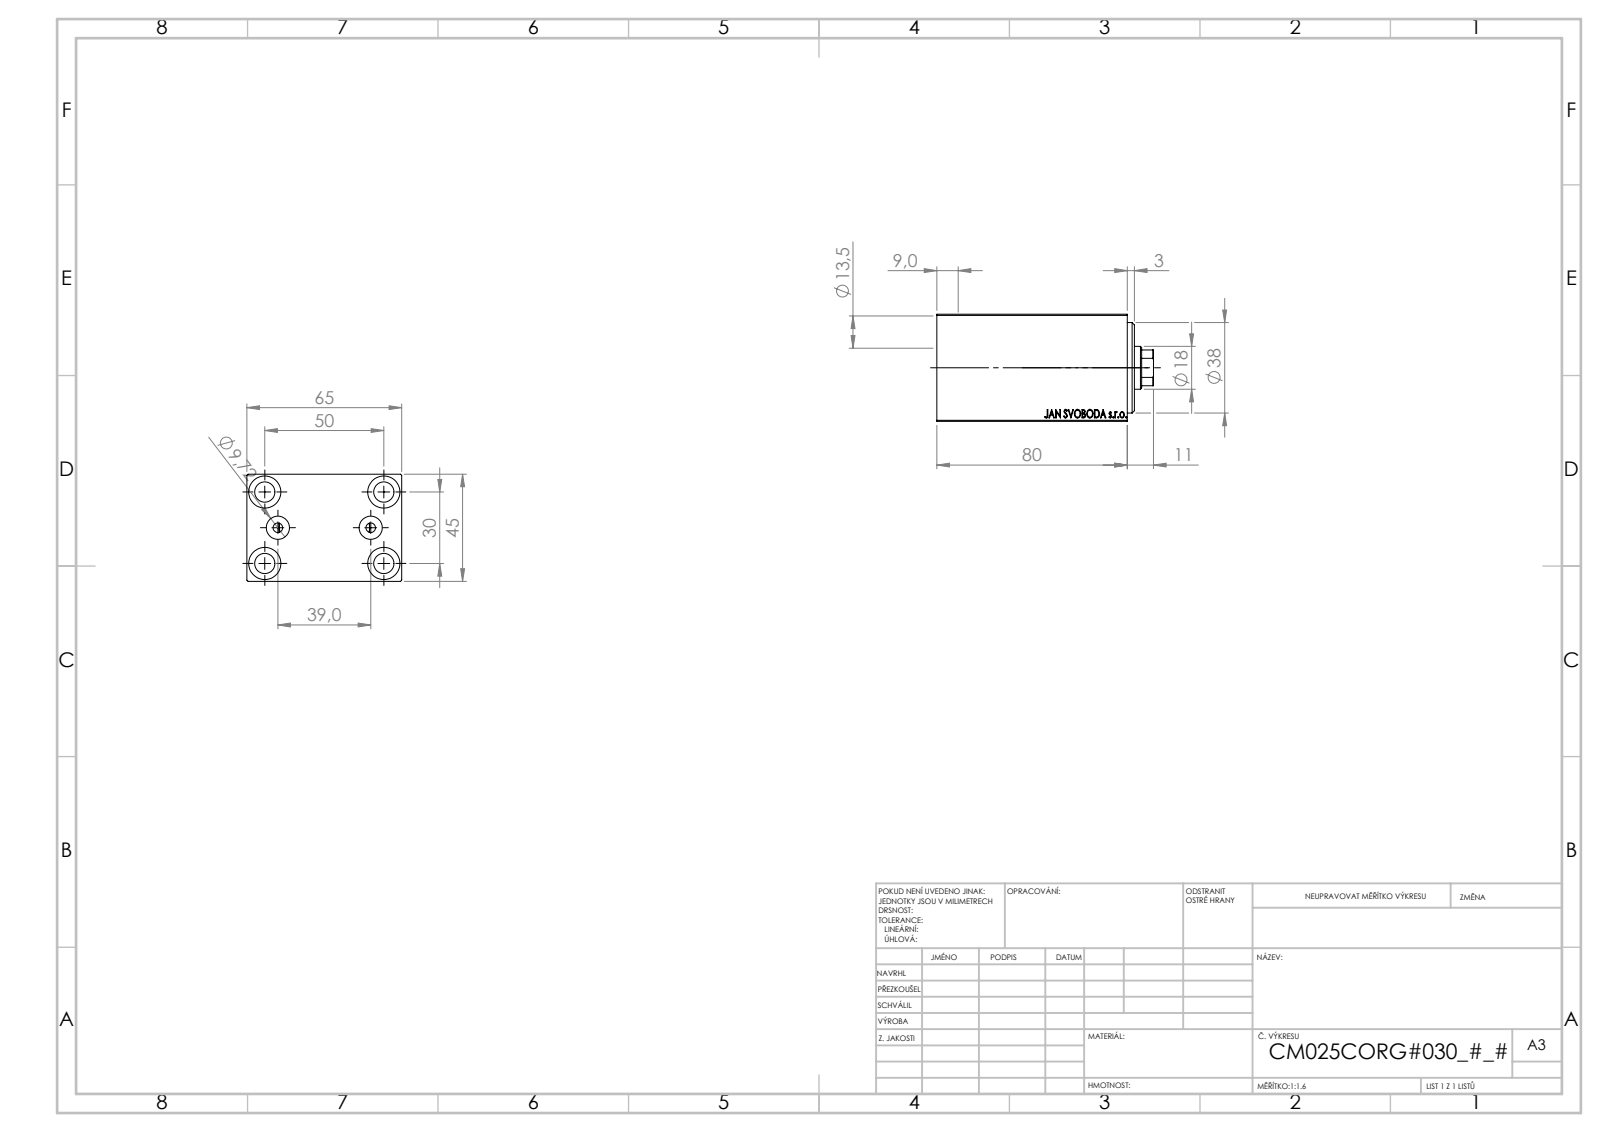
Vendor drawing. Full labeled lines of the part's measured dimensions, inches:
Part name (STEP PRODUCT): V450CM_C_VCP; V450CM_VC_B; V450CM_C_Body
STEP written by: SolidWorks 2019 (CONFIG_CONTROL_DESIGN)
Units: inches
Bodies: 3 solids, 858 faces (408 planar, 56 cylindrical, 394 other)
Overall size (bounding box): 3.583 × 2.559 × 1.772
Volume: 12.41 in³ · Surface area: 75.44 in²
Round holes (diameter × count): ⌀0.335 ×5, ⌀0.531 ×4, ⌀0.157 ×2, ⌀0.383 ×2, ⌀0.709 ×1, ⌀0.846 ×1, ⌀0.984 ×1, ⌀1.063 ×1, ⌀1.496 ×1
Partial cylindrical surfaces — rounded edges, fillets, slot ends (radius × count): R0.335 ×1
Main face-to-face distances: 1.772, 2.559, 0.197, 2.953, 3.15, 0.984, 2.165, 1.969, 0.315, 0.354
Hole centre spacings: 0.629, 1.148, 1.849, 0.768, 1.181, 1.969, 2.296, 1.535
